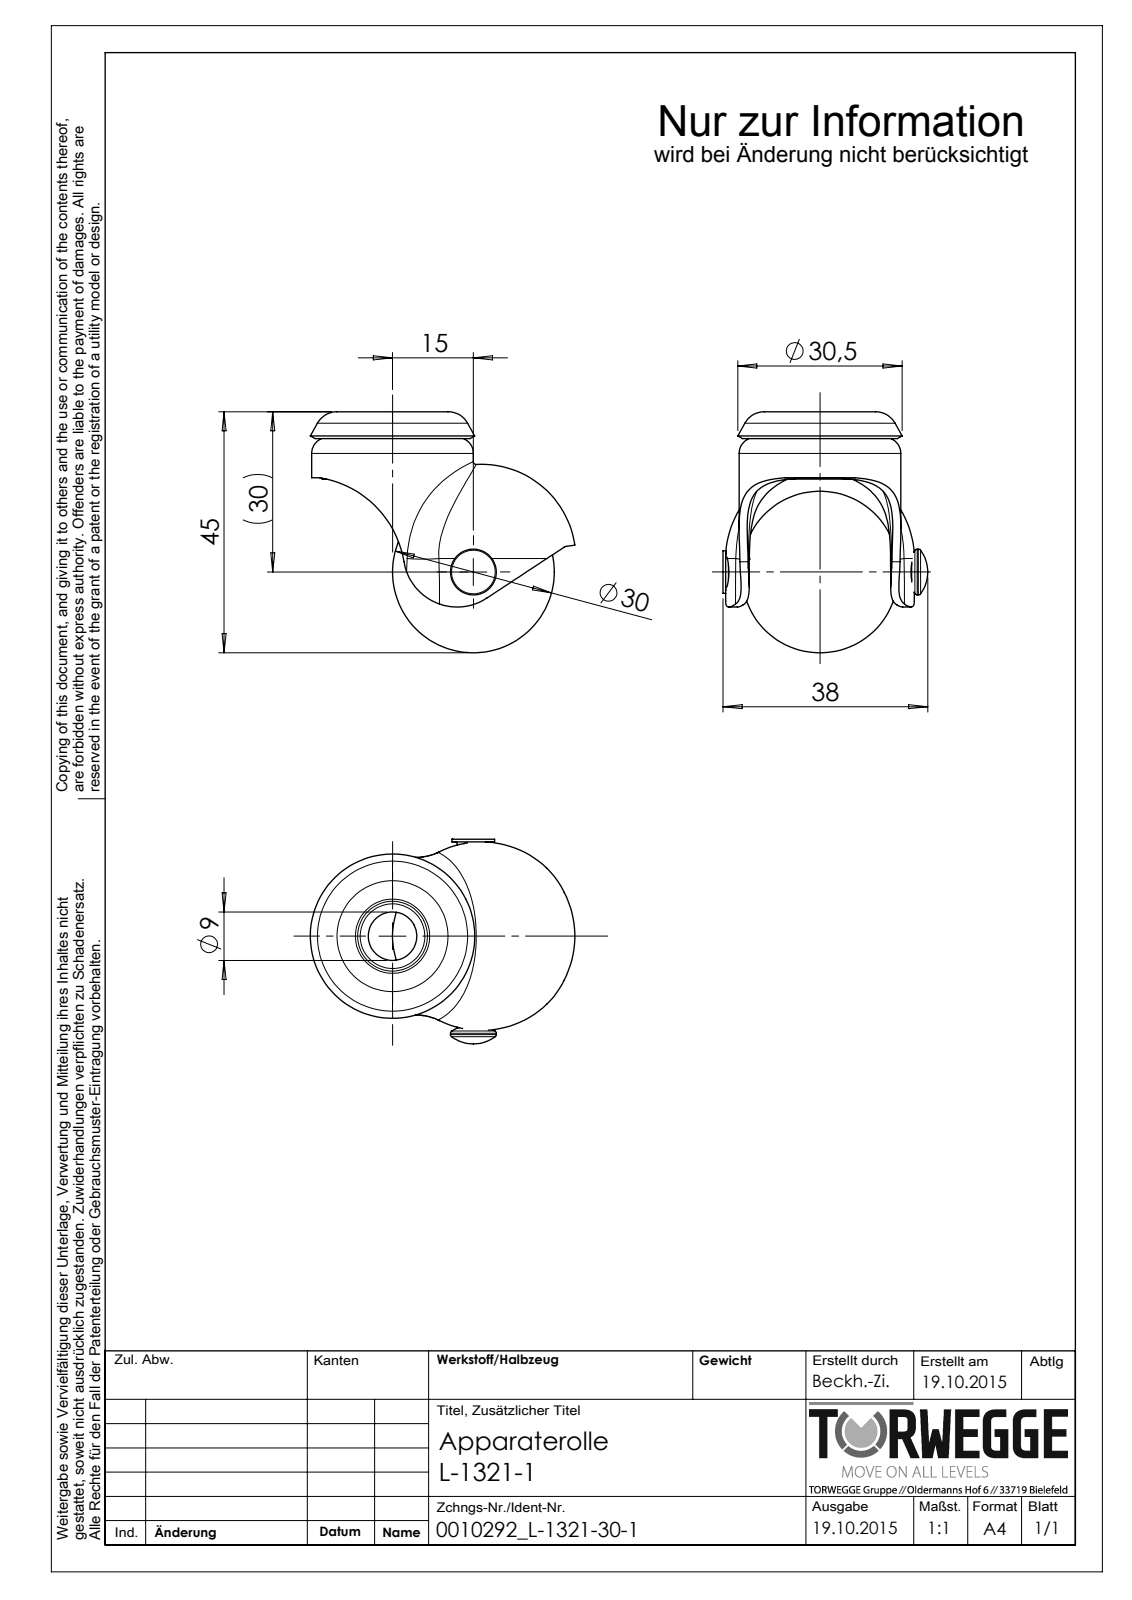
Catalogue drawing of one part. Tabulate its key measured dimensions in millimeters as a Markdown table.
| quantity | value |
| --- | --- |
| part name | 0010292_L-1321-30-1 |
| STEP written by | SolidWorks 2014 (AUTOMOTIVE_DESIGN) |
| units | millimeters |
| bodies | 7 solids, 121 faces (14 planar, 36 cylindrical, 71 other) |
| overall size | 49.07 × 44.76 × 38 |
| volume | 19 811 mm³ |
| surface area | 13 270 mm² |
| round holes (diameter × count) | 4 × 1, 6 × 1, 6.1 × 1, 9 × 1, 11.2 × 1, 27 × 1 |
| round bosses / shafts (diameter × count) | 30 × 1, 26.1 × 1, 11 × 1, 8.5 × 1, 7.9 × 1, 5.9 × 1 |
| partial cylindrical surfaces (radius × count) | 1 × 1, 10 × 1, 16 × 1, 17.5 × 1, 18.87 × 1 |
| main face-to-face distances | 27.5, 3.76, 0.76, 3, 5.74, 6.5, 9.5, 10.5, 4.76, 4 |
